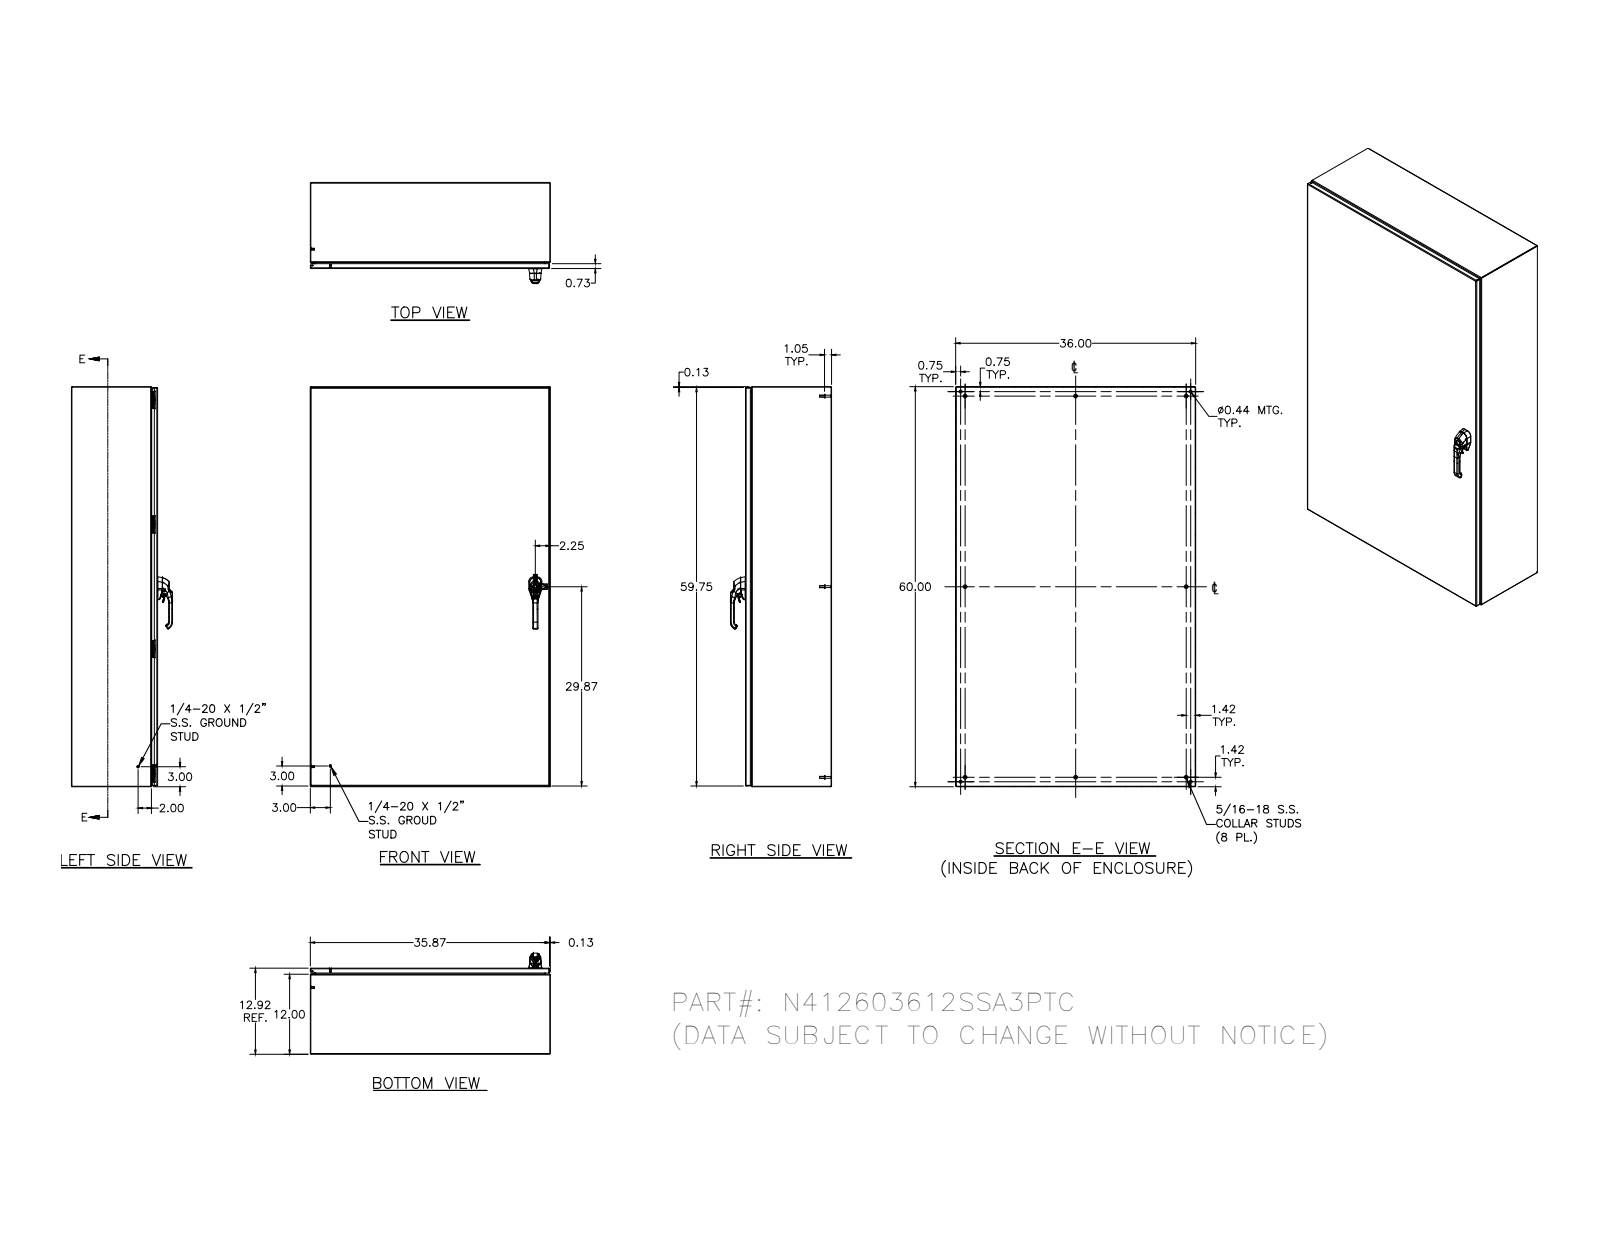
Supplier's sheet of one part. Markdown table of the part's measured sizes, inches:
| quantity | value |
| --- | --- |
| part name | N412603612SSA3PTC; N412603612SSA3PTCBTB; N4126012SSA3PTCLS; N4126012SSA3PTCRS (+8 more) |
| STEP written by | Autodesk Inventor 2011 (AUTOMOTIVE_DESIGN) |
| units | inches |
| bodies | 87 solids, 3972 faces (1320 planar, 1471 cylindrical, 1181 other) |
| overall size | 60 × 36 × 15.166 |
| volume | 531.2 in³ |
| surface area | 14 236 in² |
| round holes (diameter × count) | 0.093 × 8, 0.152 × 8, 0.167 × 8, 0.172 × 8, 0.187 × 8, 0.165 × 5, 0.156 × 4, 0.197 × 4, 0.437 × 4, 0.213 × 3, 0.106 × 2, 0.16 × 2 |
| round bosses / shafts (diameter × count) | 0.25 × 18, 0.563 × 8, 0.36 × 8, 0.32 × 8, 0.3 × 8, 0.275 × 8, 0.256 × 8, 0.164 × 8 |
| partial cylindrical surfaces (radius × count) | 0.02 × 187, 0.012 × 101, 0.05 × 50, 0.031 × 36, 0.016 × 34, 0.125 × 32, 0.019 × 23, 0.118 × 23 |
| main face-to-face distances | 0.074, 12.843, 12.769, 12.917, 35.926, 59.926, 35.852, 36, 59.852, 60 |
| hole center spacings | 18.667, 37.333, 18.667, 56, 37.333, 0.5, 0.656, 18.673 |
